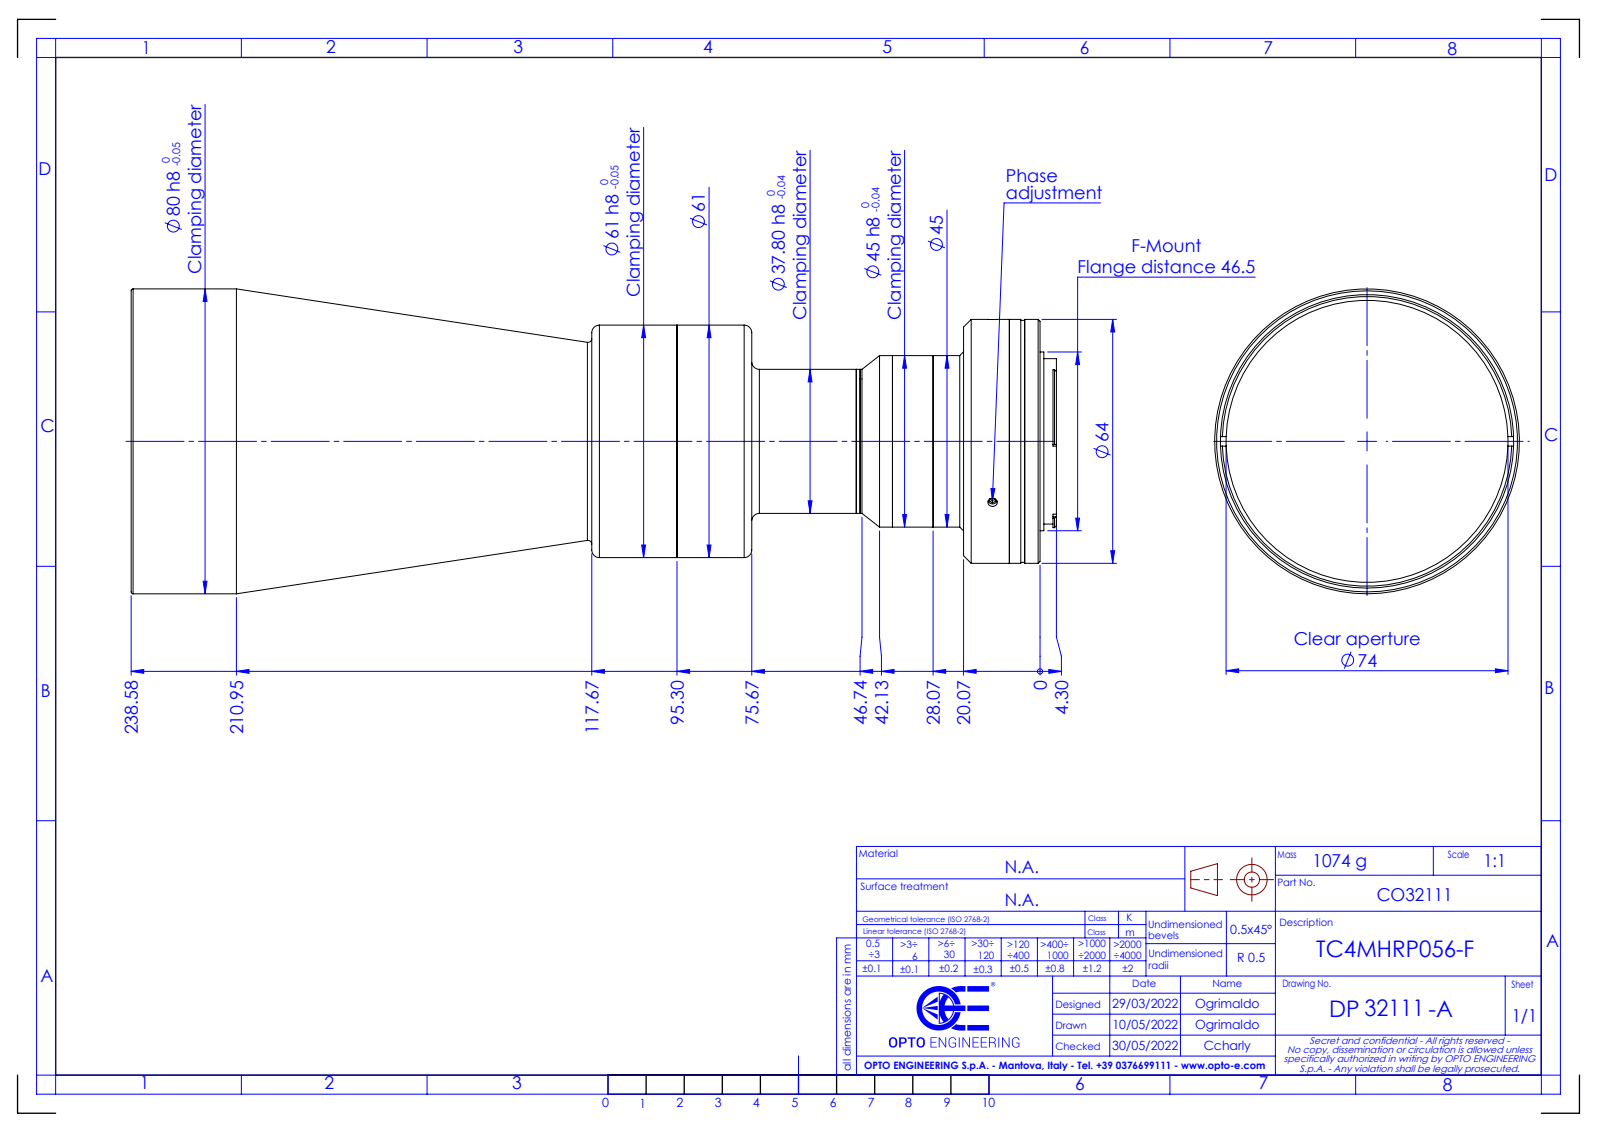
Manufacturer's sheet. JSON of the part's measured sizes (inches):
{"part_name": "DP32111-A_TC4MHRP056-F", "step_written_by": "SolidWorks 2021 (CONFIG_CONTROL_DESIGN)", "units": "inches", "bodies": {"solids": 0, "faces": 152, "planar": 51, "cylindrical": 63, "other": 38}, "overall_size": [9.562, 3.15, 3.15], "round_holes": [[0.098, 3], [1.142, 1], [1.26, 1], [1.654, 1], [2.087, 1], [2.913, 1], [3.031, 1]], "round_bosses_or_shafts": [[3.15, 1], [2.52, 1], [2.5, 1], [2.402, 1], [1.846, 1], [1.772, 1], [1.709, 1], [1.488, 1]], "partial_cylinders_radius": [[0.02, 6], [0.045, 2], [0.892, 1]], "face_to_face_distances": [0.199, 0.591, 0.79, 0.633, 0.041, 0.157, 2.189, 2.781, 2.822, 2.98]}
